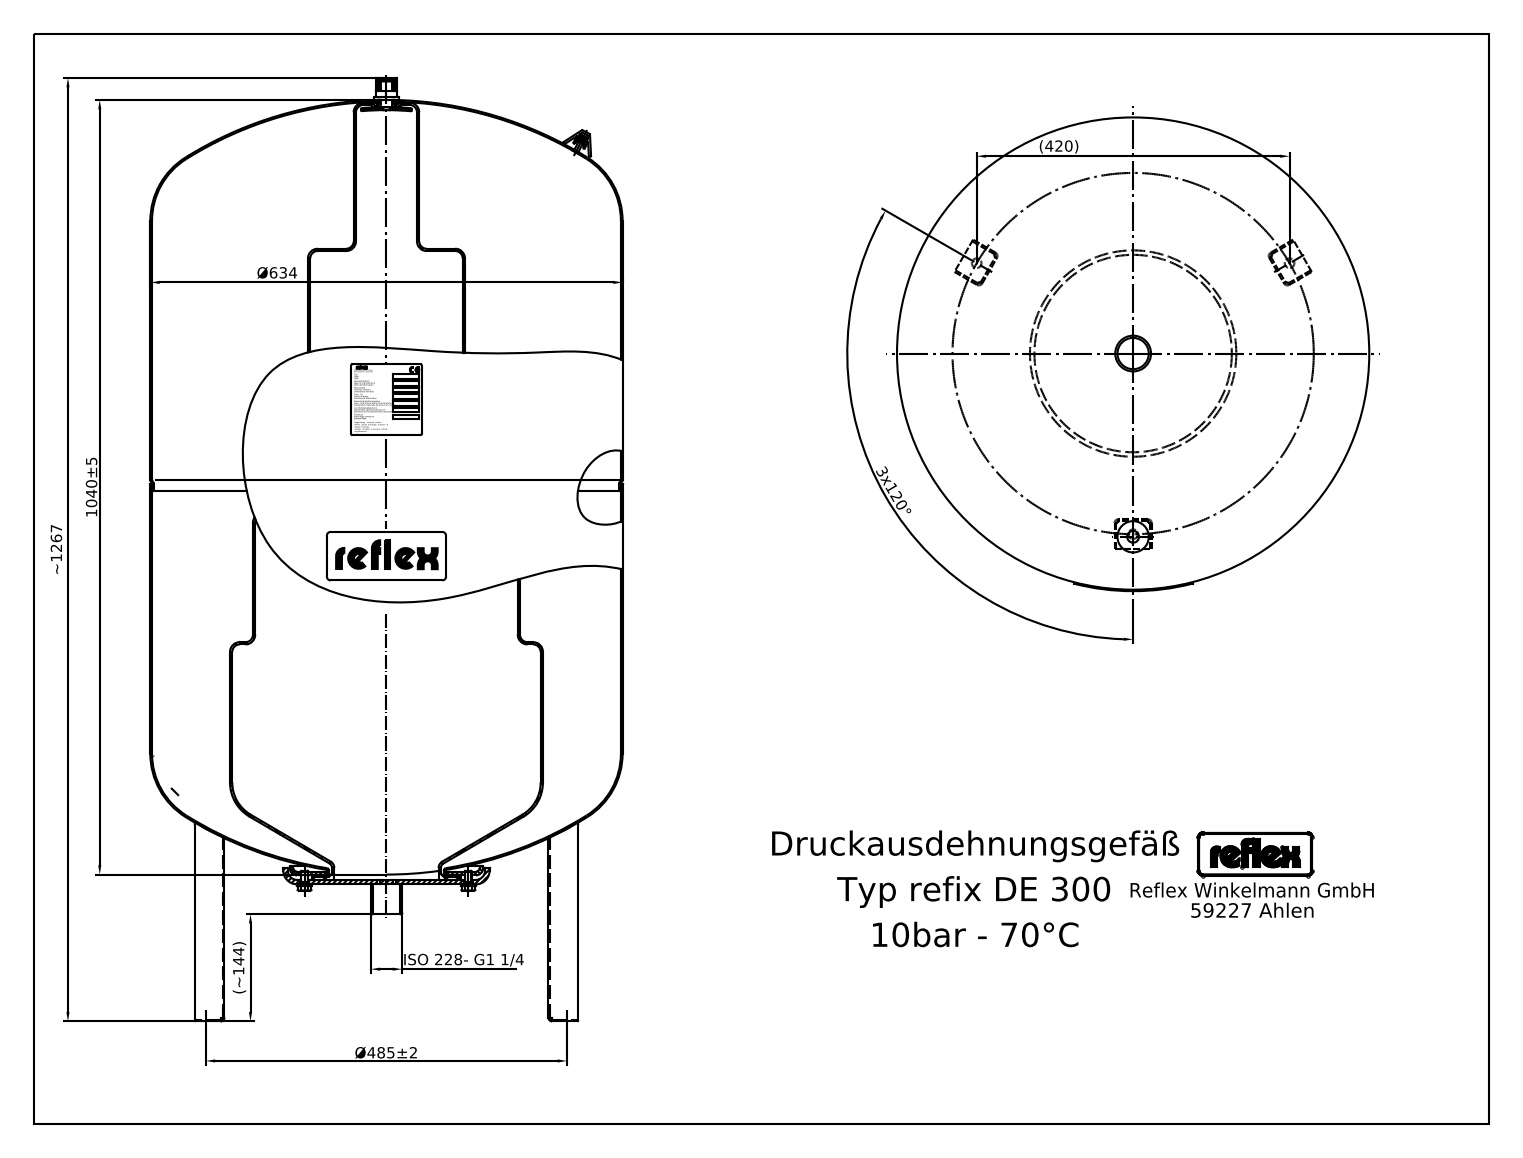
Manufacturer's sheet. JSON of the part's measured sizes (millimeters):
{"step_written_by": "Mechanical Desktop 2008 (CONFIG_CONTROL_DESIGN)", "units": "millimeters", "bodies": {"solids": 17, "faces": 394, "planar": 181, "cylindrical": 139, "other": 74}, "overall_size": [1267, 634, 634], "volume_mm3": 294100000, "surface_area_mm2": 4018000, "round_holes": [[13.4, 3], [14.1, 1], [157, 1], [250, 1]], "round_bosses_or_shafts": [[10, 8], [634, 1], [260, 1], [230, 1], [42.4, 1], [34, 1], [17.1, 1], [16, 1]], "partial_cylinders_radius": [[1, 15], [2.5, 15], [5, 15], [5.62, 4], [2.25, 3], [3.84, 2], [6.75, 2], [9.27, 2]], "face_to_face_distances": [716, 2.5, 47.5, 170, 886, 6, 176, 892, 45, 50], "hole_center_spacings": [242.5, 420.02]}
